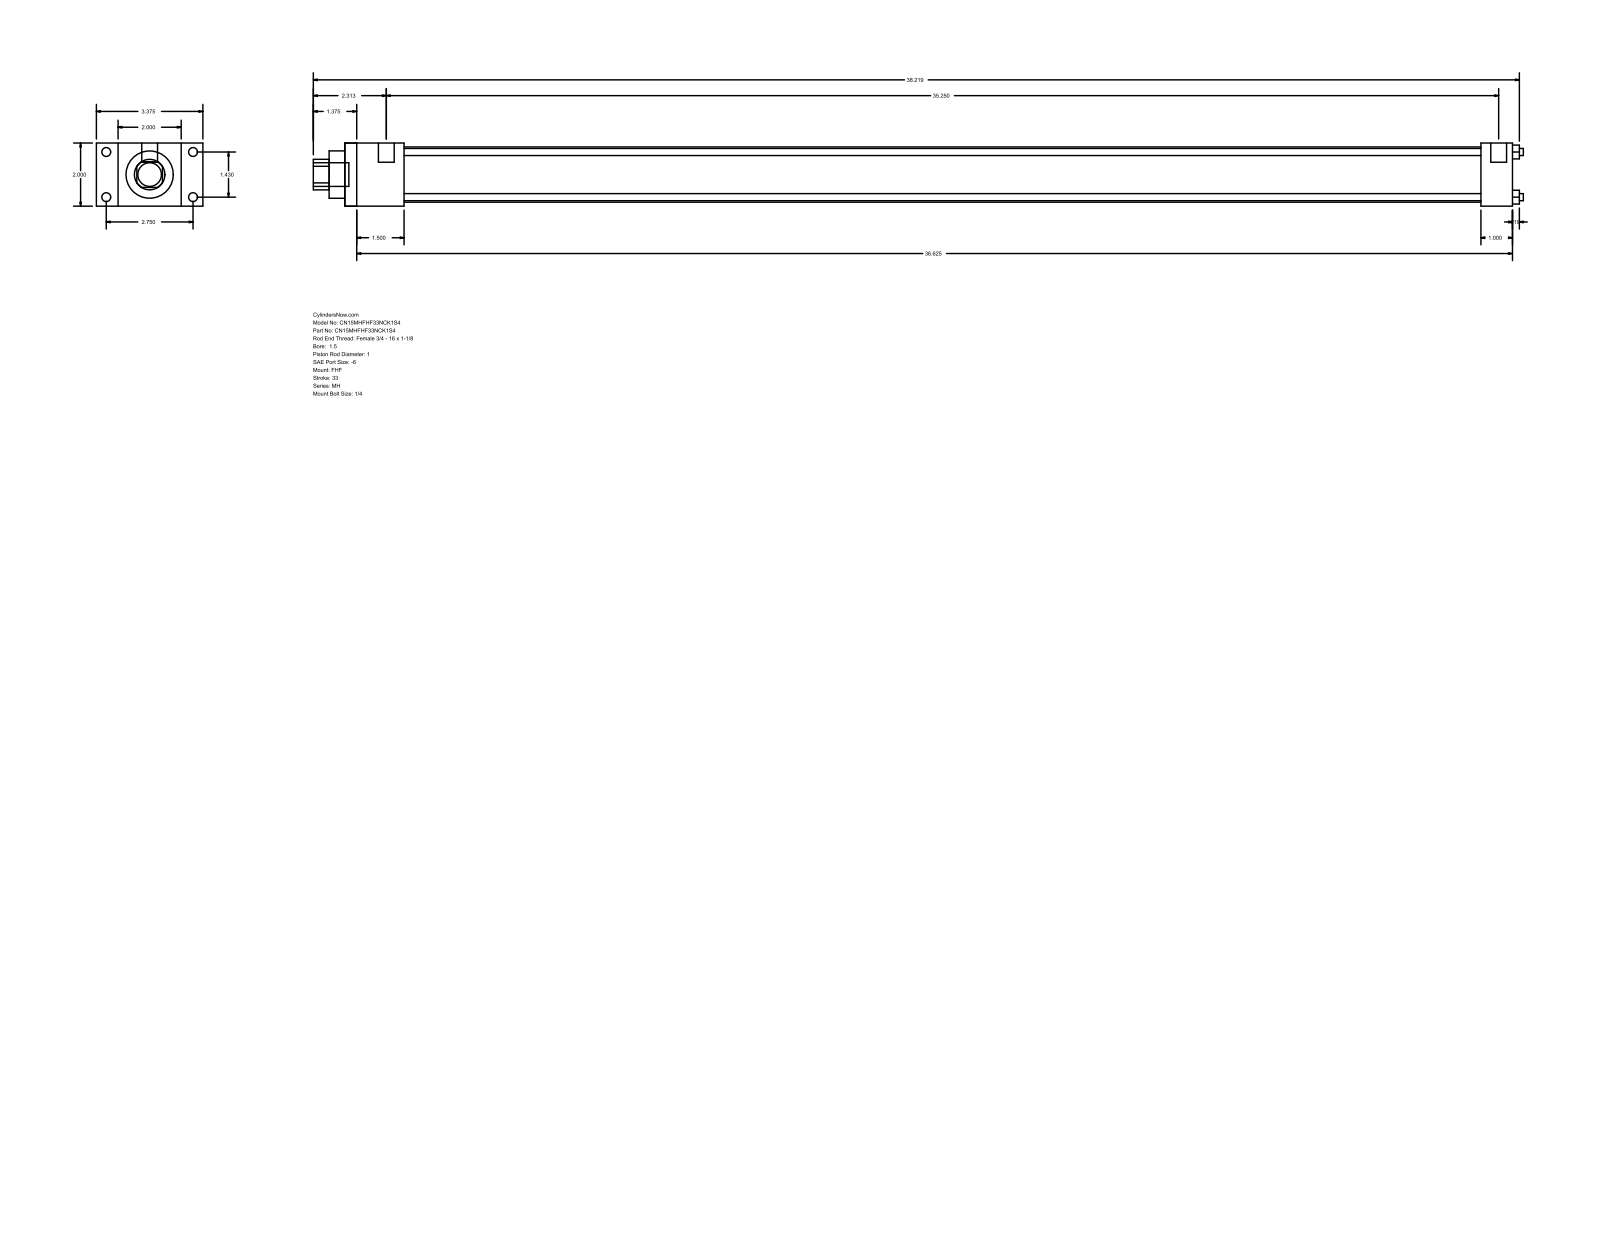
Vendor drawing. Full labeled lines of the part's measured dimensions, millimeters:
Part name (STEP PRODUCT): MH_FHF__0150_1
STEP written by: GSSL Pune (CONFIG_CONTROL_DESIGN)
Units: millimetres
Bodies: 0 solids, 88 faces (60 planar, 28 cylindrical, 0 other)
Overall size (bounding box): 973.93 × 85.72 × 50.8
Round holes (diameter × count): ⌀5.71 ×4, ⌀25.4 ×1, ⌀38.1 ×1, ⌀44.45 ×1
Round bosses / shafts (diameter × count): ⌀7.14 ×4, ⌀5.56 ×4, ⌀12.7 ×2, ⌀19.05 ×1
Partial cylindrical surfaces — rounded edges, fillets, slot ends (radius × count): R12.29 ×1
Main face-to-face distances: 50.8, 17.46, 68.26, 47.63, 85.72, 939.8, 892.17, 25.4, 914.4, 866.77
Hole centre spacings: 25.68, 36.32, 51.36
